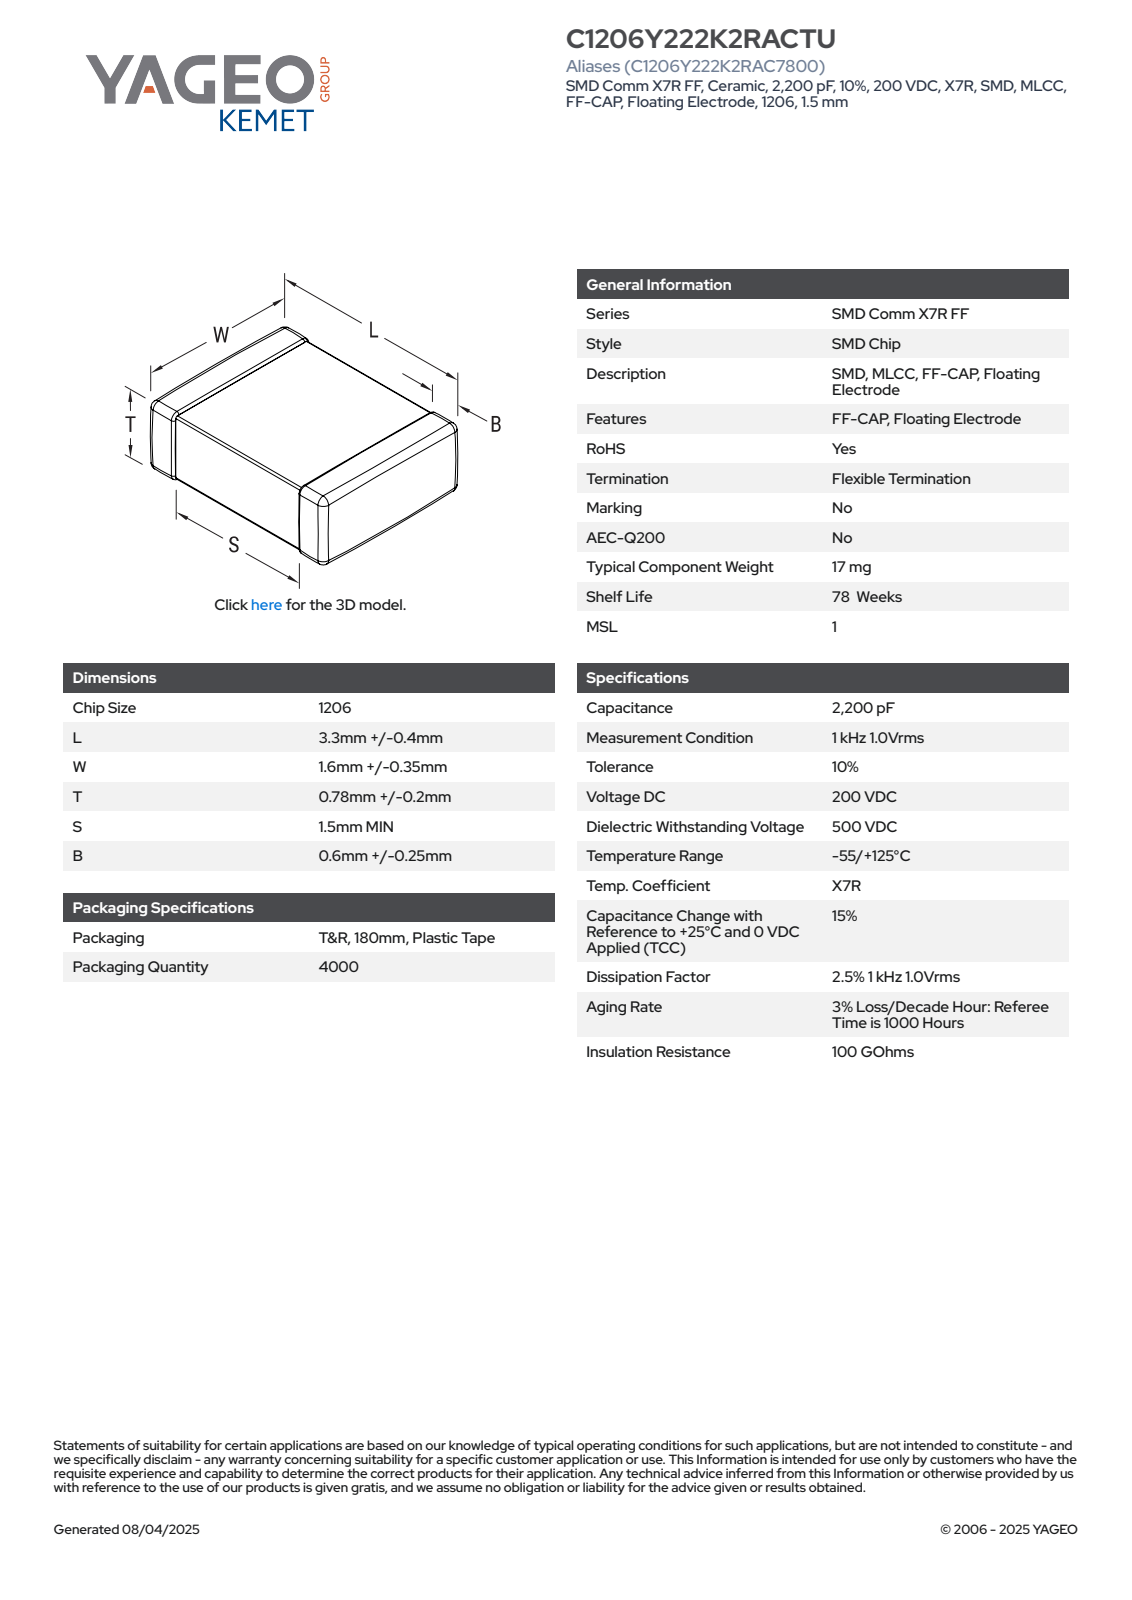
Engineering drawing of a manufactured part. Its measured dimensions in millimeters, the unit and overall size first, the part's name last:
Units: millimetres
Overall size (bounding box): 3.7 × 1.95 × 0.98
Main face-to-face distances: 0.94, 0.9, 0.98, 1.91, 3.7, 1.87, 1.95, 1.71, 1.99, 2
Volume: 7 mm³ · Surface area: 25 mm²
Bodies: 4 solids, 129 faces (71 planar, 42 cylindrical, 16 other)
Part name (STEP PRODUCT): CCS_CCSTD_1206_L3.7W1.95T0.98B0.6
STEP written by: SolidWorks 2021 (AUTOMOTIVE_DESIGN)
